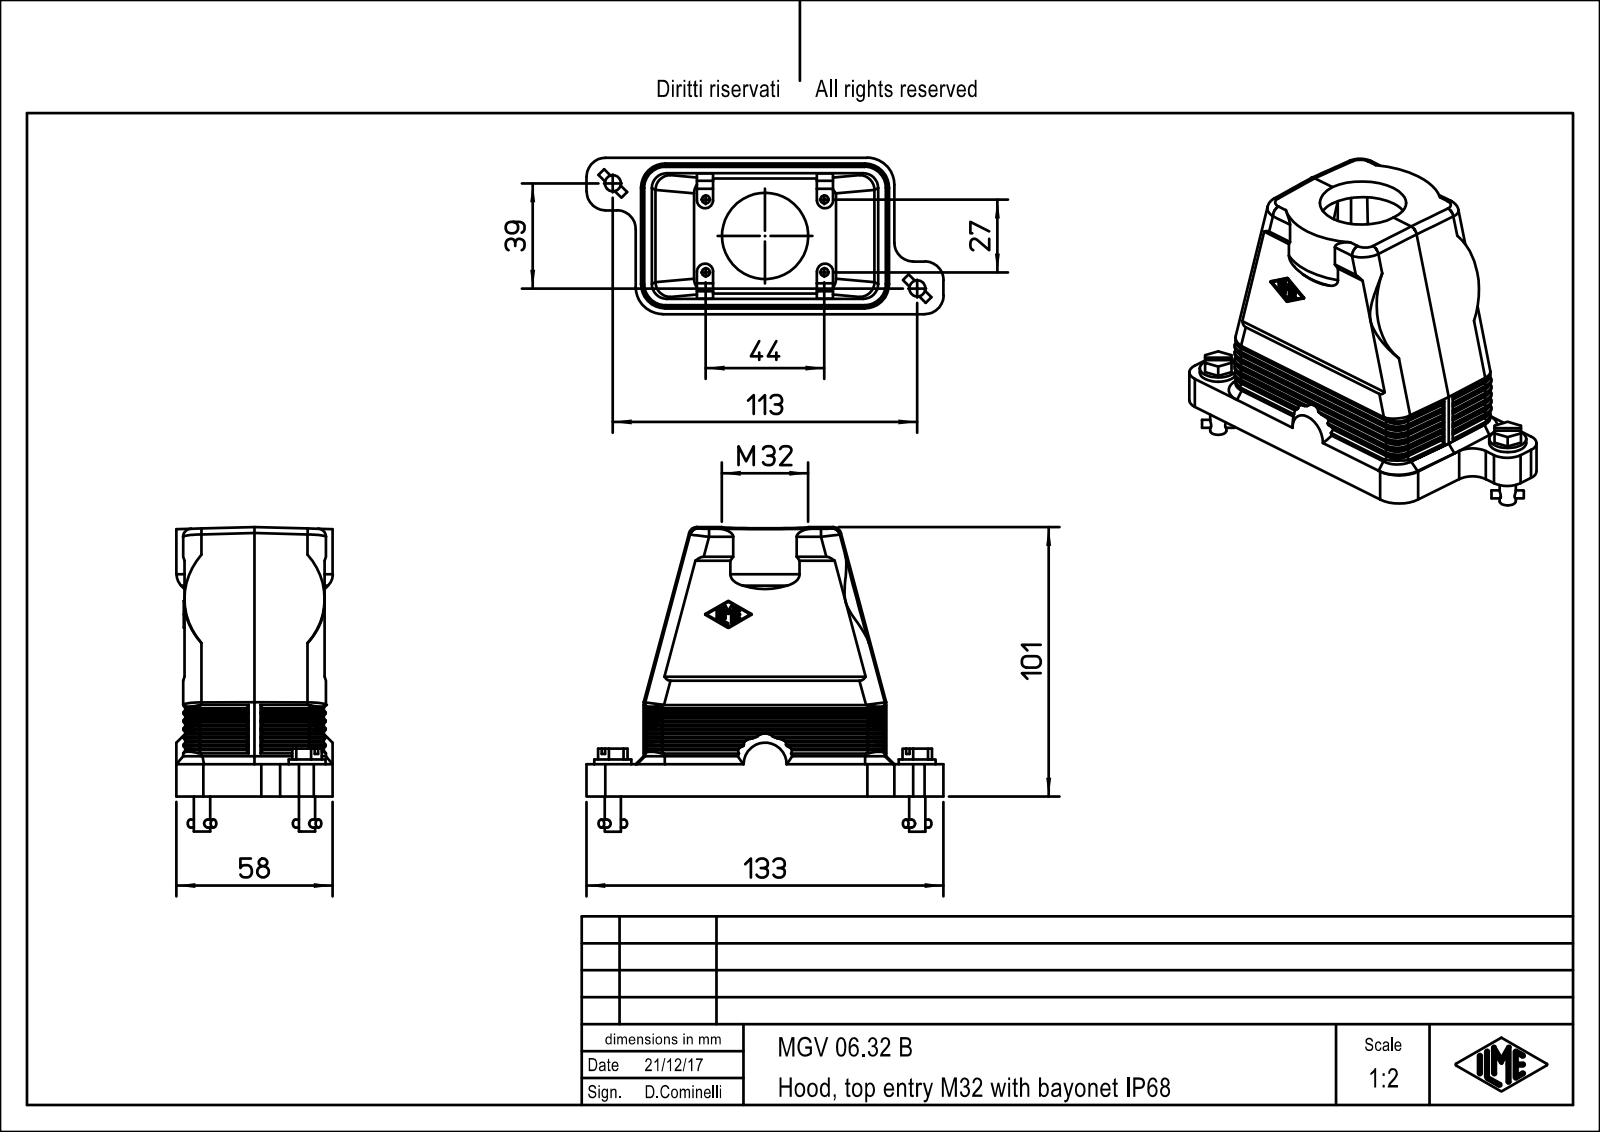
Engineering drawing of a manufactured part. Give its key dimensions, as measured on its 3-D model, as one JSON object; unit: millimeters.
{"part_name": "MGV_06.32_B", "step_written_by": "PTC Creo Elements/Direct Modeling 19.0E 27-Jun-2016 (C) Parametric Technology GmbH (AUTOMOTIVE_DESIGN)", "units": "millimeters", "bodies": {"solids": 1, "faces": 544, "planar": 260, "cylindrical": 135, "other": 149}, "overall_size": [132.5, 113, 58], "volume_mm3": 129006, "surface_area_mm2": 63848, "round_holes": [[3, 4], [32, 1]], "round_bosses_or_shafts": [[13.7, 2], [6, 2], [3, 2]], "partial_cylinders_radius": [[7, 62], [0.33, 15], [5.5, 8], [3, 4], [8.5, 4], [0.17, 3], [10, 2], [0.67, 1]], "face_to_face_distances": [6, 44.5, 3, 55, 52, 2.5, 3.33, 0.5, 55.5, 52.5], "hole_center_spacings": [25.81, 27, 44, 51.62]}
